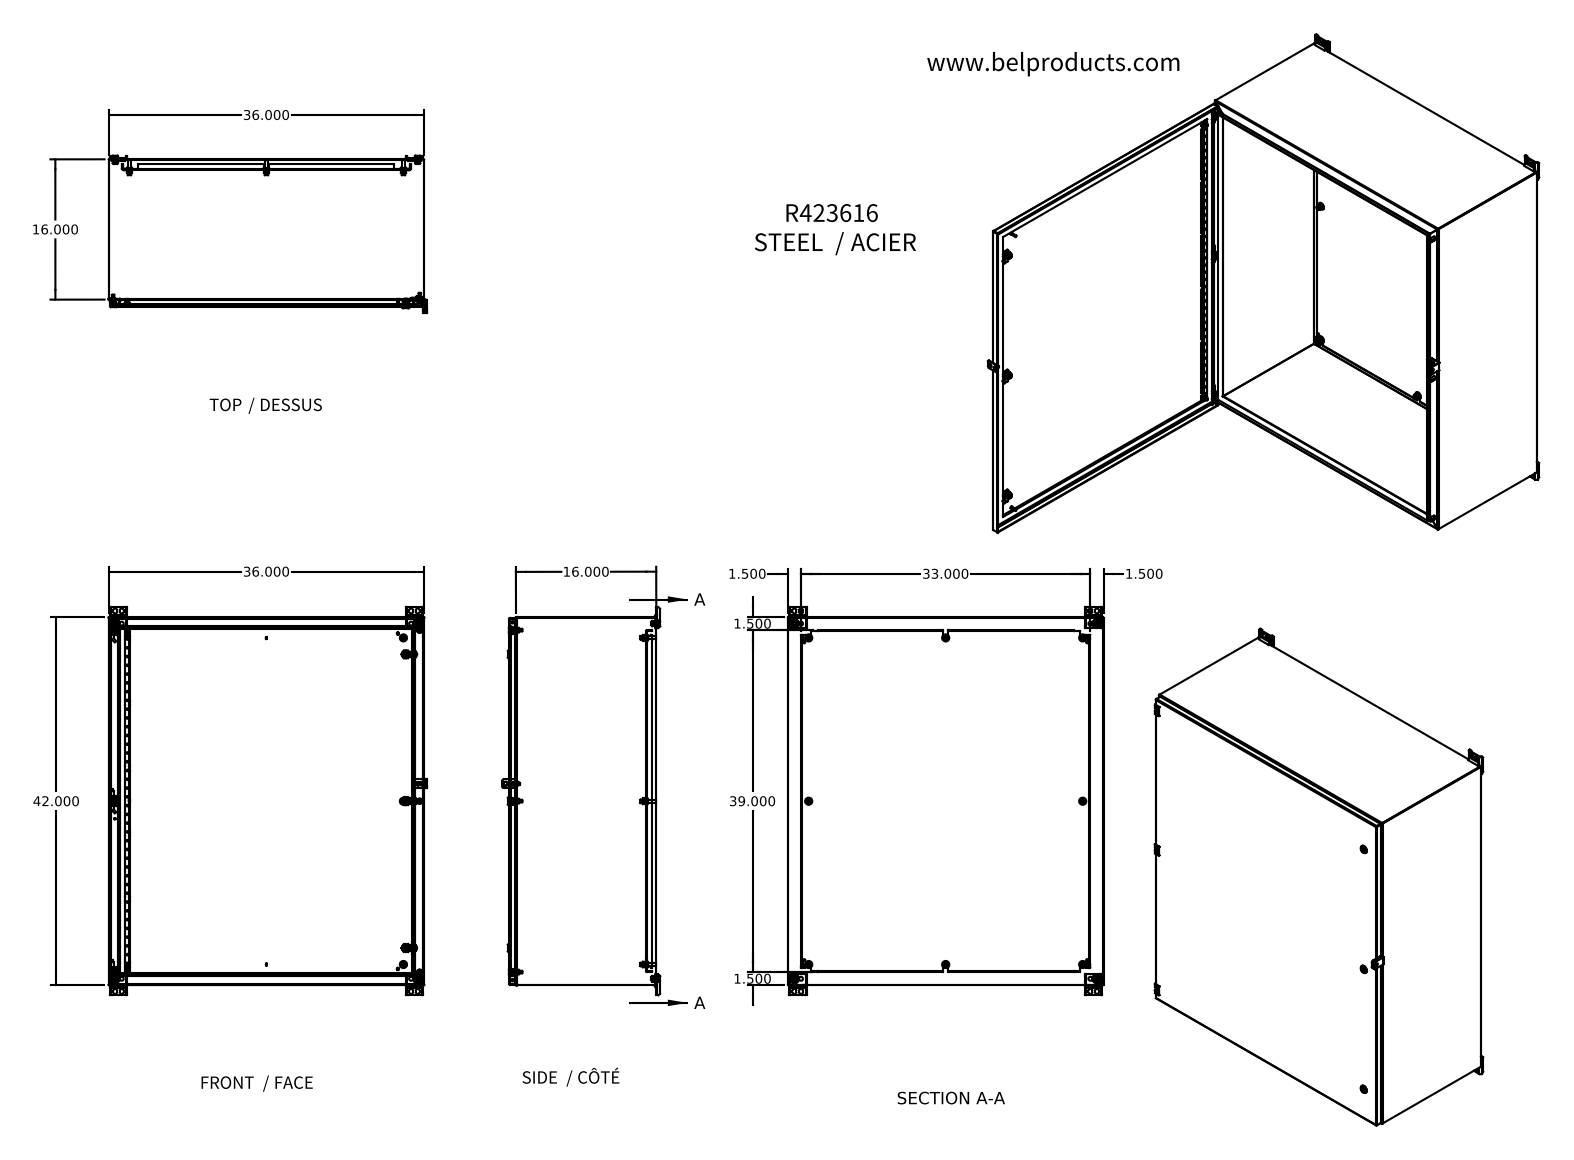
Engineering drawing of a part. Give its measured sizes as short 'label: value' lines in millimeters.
name: 0.375 DIA; CAOUTCHOUC; METAL; LOCK AVEC TOURNEVIS TYPE 4-12 SANS CAME (+8 more)
written by: Unknown (AUTOMOTIVE_DESIGN)
unit: mm
bodies: 124 solids, 4941 faces (2773 planar, 898 cylindrical, 1270 other)
size: 1124.36 × 921.56 × 457.07
volume: 9 124 000 mm³; area: 9 718 000 mm²
holes: 38× ⌀4.68, 14× ⌀3.17, 12× ⌀9.53, 12× ⌀10.31, 8× ⌀11.58, 6× ⌀0.35, 6× ⌀6.73, 5× ⌀7.14, 4× ⌀4.04, 4× ⌀4.83, 4× ⌀5.99, 4× ⌀9.02
bosses: 14× ⌀3.02, 12× ⌀20.62, 8× ⌀16.19, 8× ⌀8.97, 8× ⌀0.79, 5× ⌀4.83, 4× ⌀6.5, 4× ⌀5.92
rounds: 121× R0.2, 32× R9.53, 28× R0.81, 26× R0.3, 24× R0.25, 16× R5.79, 12× R2.34, 12× R3.48
face distances: 1.52, 1.91, 424.59, 423.07, 424.98, 426.5, 912.88, 2.67, 397.01, 395.1
hole spacings: 473.07, 497.51, 516, 617.5, 13.09, 15.87, 19.84, 38.11
